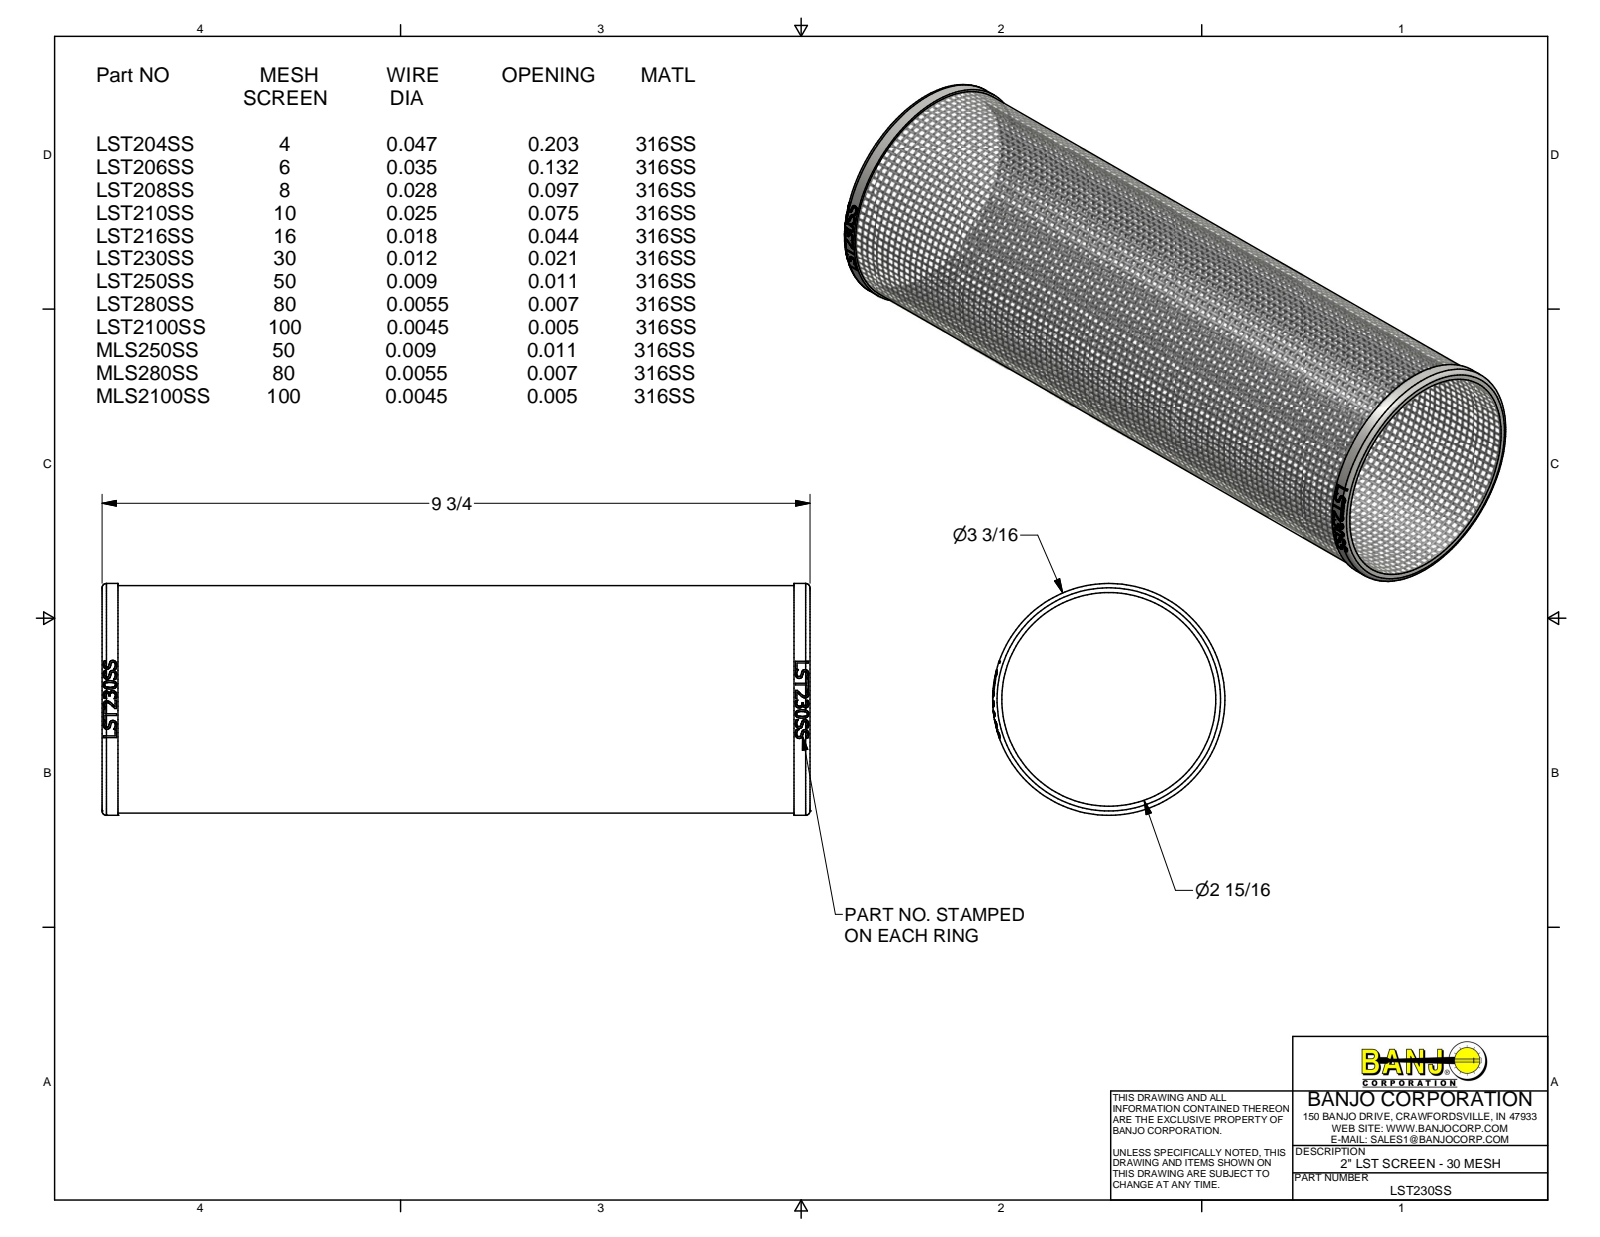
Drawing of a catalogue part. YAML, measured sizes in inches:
part_name: "LST230SS"
step_written_by: "Autodesk Inventor 2013 (AUTOMOTIVE_DESIGN)"
units: inches
bodies: {solids: 1, faces: 288, planar: 84, cylindrical: 22, other: 182}
overall_size: [9.72, 3.188, 3.188]
volume: 8.933
surface_area: 188
round_holes:
  - {diameter: 2.937, count: 1}
round_bosses_or_shafts:
  - {diameter: 3.188, count: 1}
  - {diameter: 3.128, count: 1}
partial_cylinders:
  - {radius: 1.574, count: 1}
face_to_face_distances: [9.72, 9.501, 0.219, 9.282, 0.303, 0.747, 0.327, 0.723, 0.024, 0.42]
